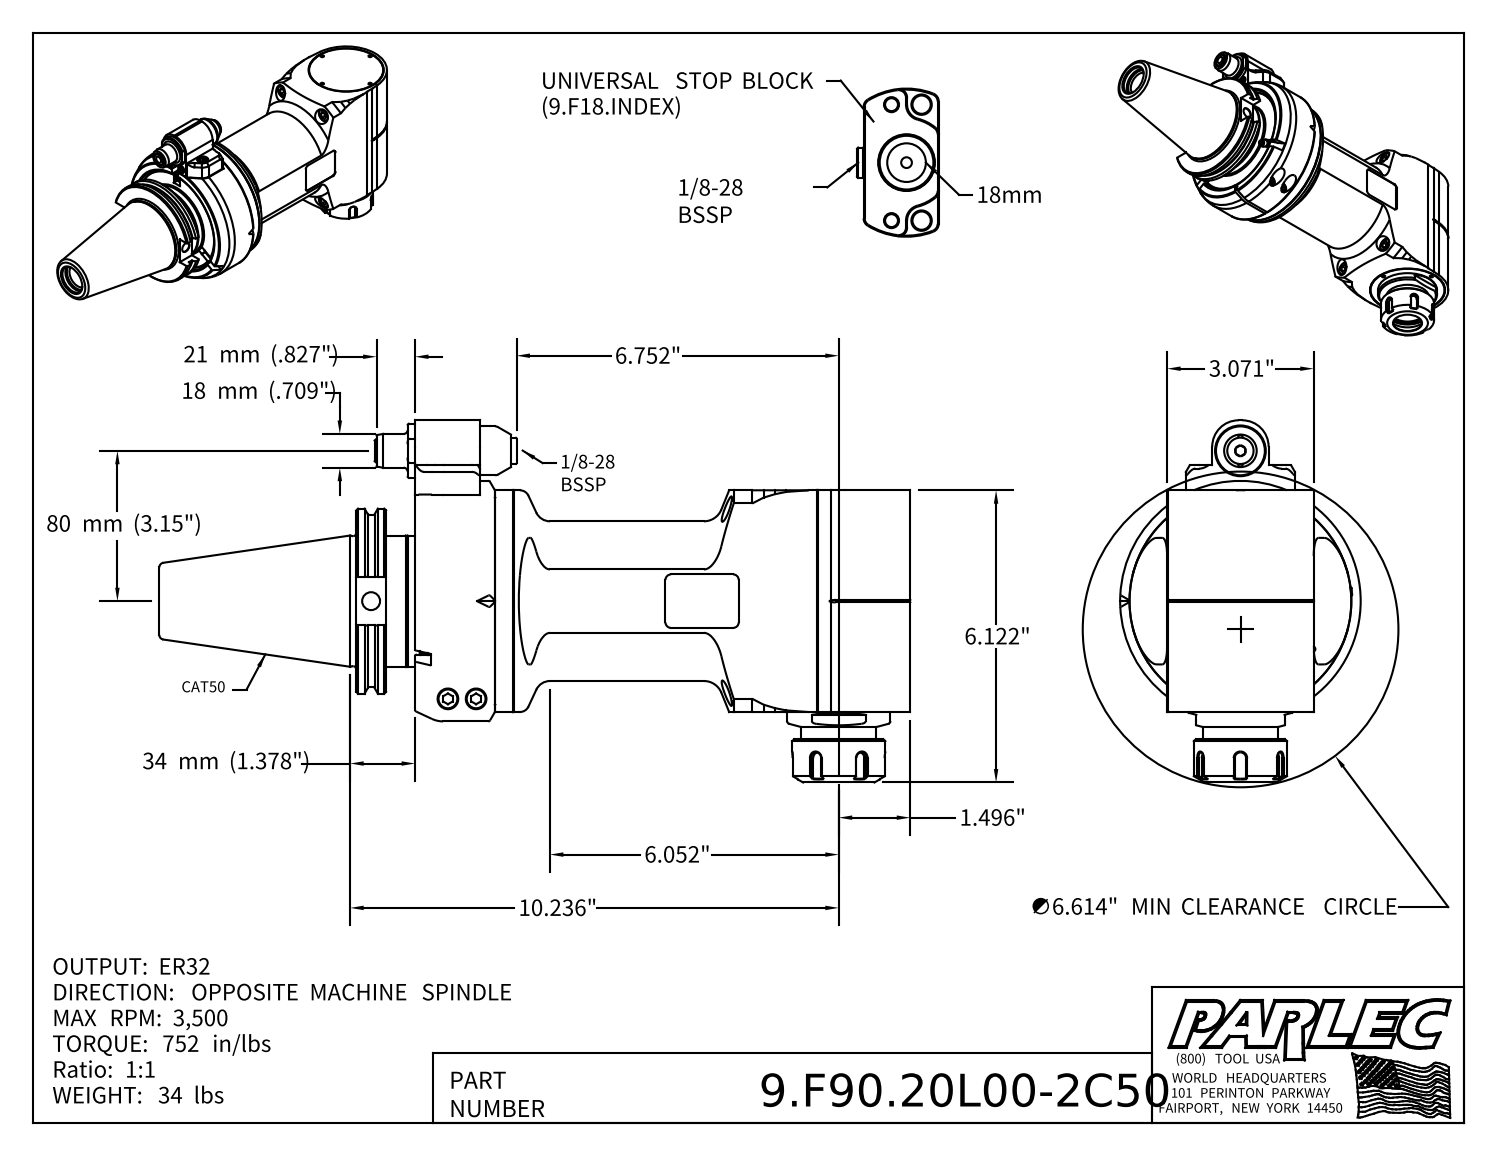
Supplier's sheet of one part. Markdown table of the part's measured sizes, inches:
| quantity | value |
| --- | --- |
| part name | 9.F90.20L00-2C50; 9_GA2_458_2; 9FL2ATC; 9CT502ATC (+5 more) |
| STEP written by | Autodesk Inventor 2022 (AUTOMOTIVE_DESIGN) |
| units | inches |
| bodies | 8 solids, 671 faces (318 planar, 151 cylindrical, 202 other) |
| overall size | 15.732 × 7.589 × 5.039 |
| volume | 155.2 in³ |
| surface area | 397.5 in² |
| round holes (diameter × count) | 0.126 × 4, 0.197 × 4, 0.531 × 4, 0.102 × 2, 0.165 × 2, 0.209 × 2, 0.315 × 2, 0.409 × 2, 0.433 × 2, 1.063 × 2, 0.098 × 1, 0.118 × 1 |
| round bosses / shafts (diameter × count) | 0.512 × 4, 0.394 × 4, 0.236 × 4, 0.709 × 2, 0.098 × 2, 5.039 × 1, 4.65 × 1, 4.646 × 1 |
| partial cylindrical surfaces (radius × count) | 0.079 × 8, 0.118 × 7, 0.157 × 4, 0.016 × 2, 0.02 × 2, 0.039 × 2, 0.138 × 2, 0.315 × 2 |
| main face-to-face distances | 3.071, 1.024, 0.02, 0.315, 1.378, 0.354, 0.236, 1.575, 1.339, 4.646 |
| hole center spacings | 1.24, 1.754, 2.203, 0.276, 0.512, 0.748, 0.923, 1.006 |
